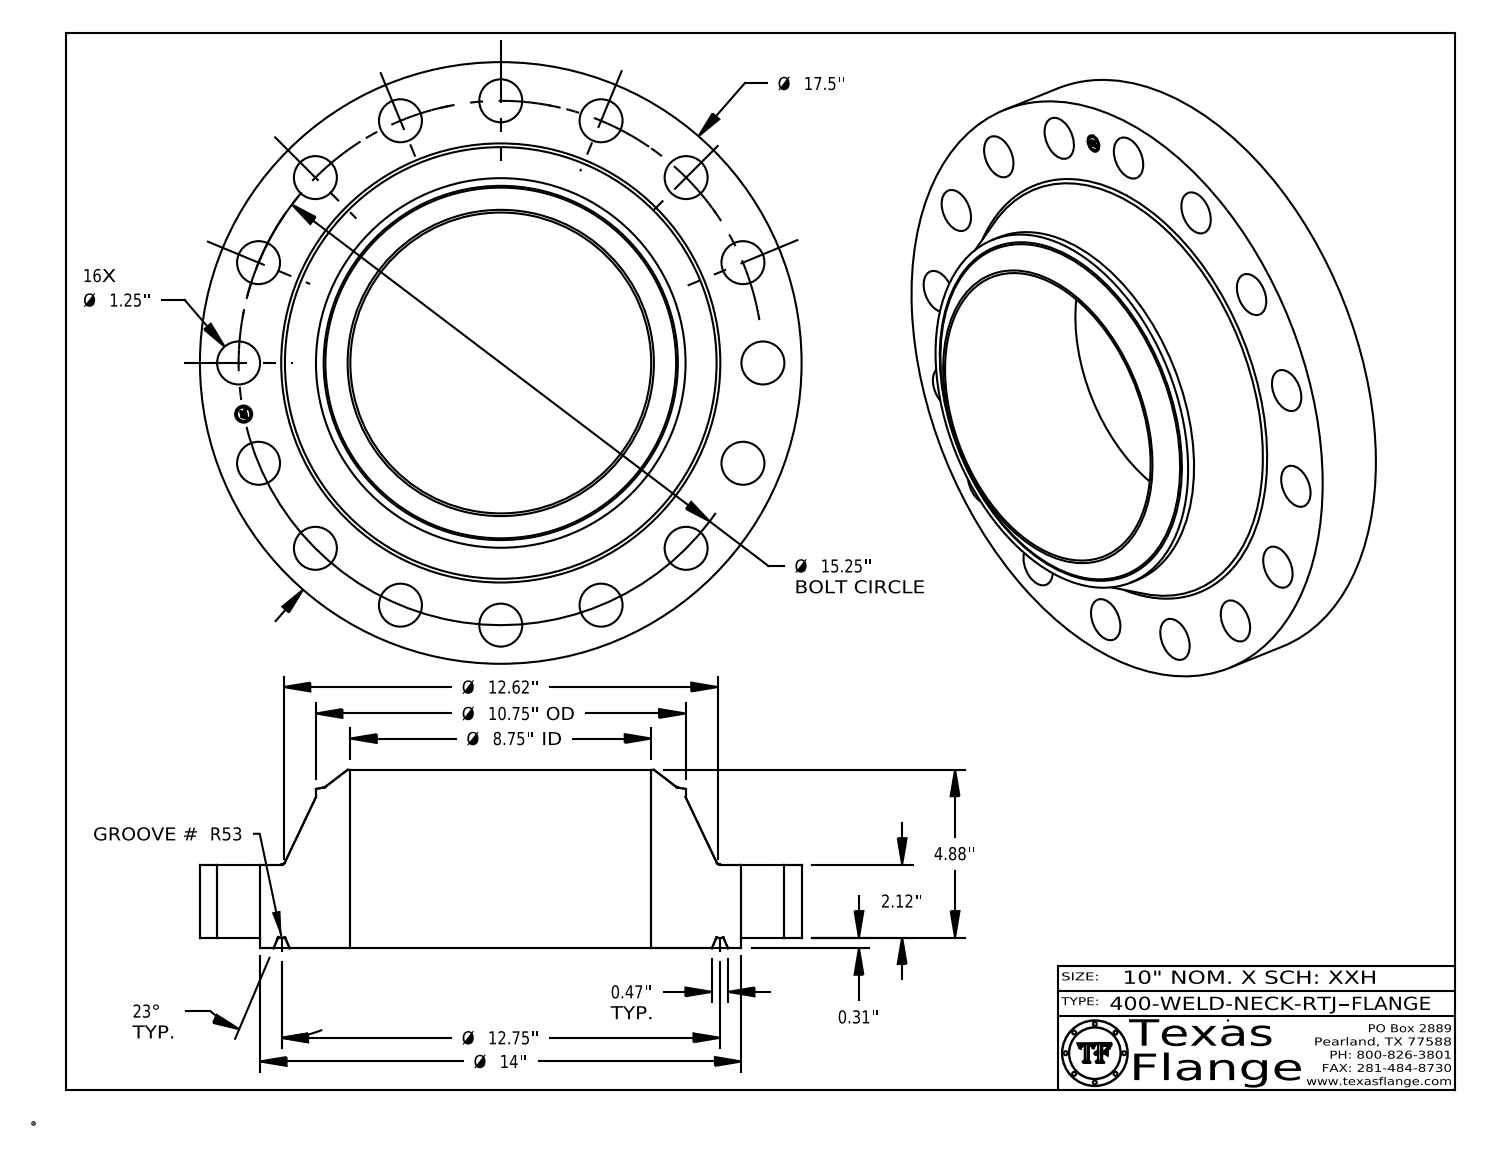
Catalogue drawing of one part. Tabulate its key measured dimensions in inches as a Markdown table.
| quantity | value |
| --- | --- |
| part name | 400-WELD-NECK-RTJ |
| STEP written by | CATIA V5 STEP AP214 (AUTOMOTIVE_DESIGN) |
| units | inches |
| bodies | 1 solid, 449 faces (371 planar, 60 cylindrical, 18 other) |
| overall size | 17.5 × 17.5 × 5.193 |
| volume | 473.6 in³ |
| surface area | 802.4 in² |
| round holes (diameter × count) | 1.25 × 16, 0.495 × 1, 8.75 × 1 |
| round bosses / shafts (diameter × count) | 0.03 × 8, 17.5 × 1, 14 × 1, 10.75 × 1, 0.39 × 1 |
| main face-to-face distances | 2.433, 0.313, 2.12, 5.193, 4.88, 2.76, 0.015, 2.418, 2.105, 2.775 |
| hole center spacings | 8.472, 10.783, 14.957, 14.089, 7.625, 2.975, 2.975, 5.836 |
